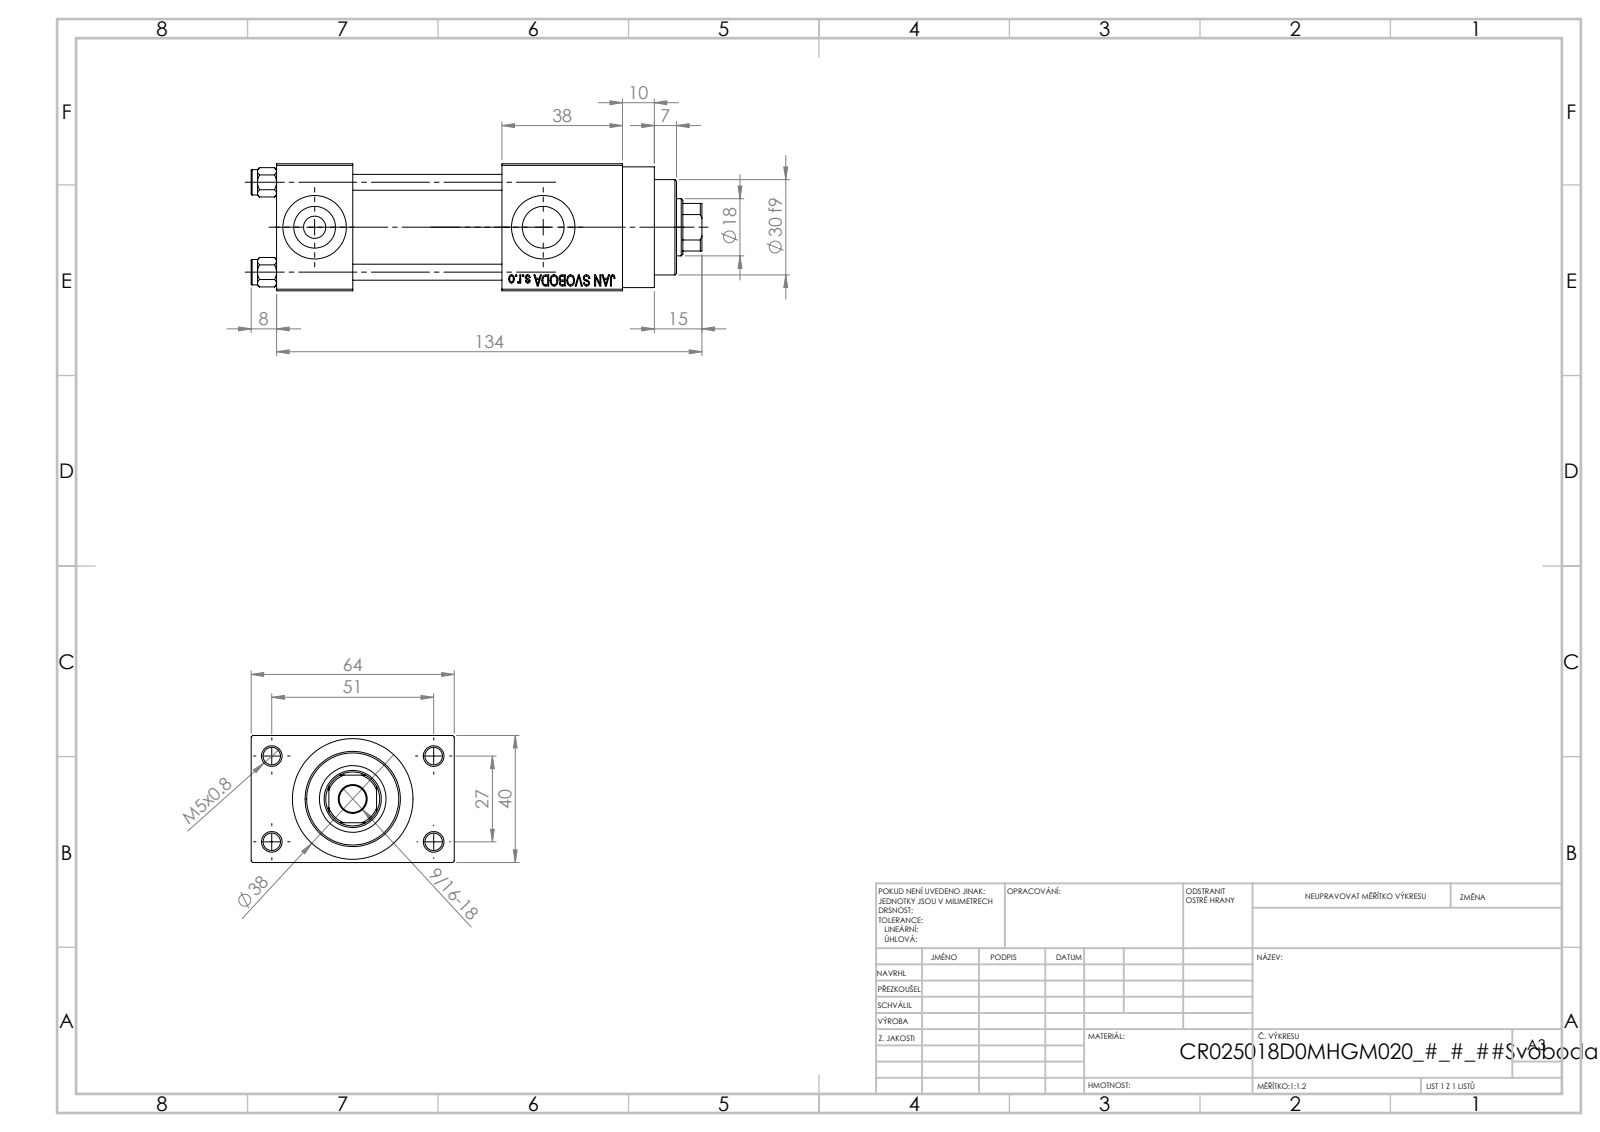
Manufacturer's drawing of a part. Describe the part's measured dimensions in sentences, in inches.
The part is named "V215CR_D_TYCINKA; NUT_M5_D; V215CR_VCP_D; V215_VC_A (+1 more)". Its 3-D file was written by "SolidWorks 2019 (CONFIG_CONTROL_DESIGN)". It is 11 solids with 1099 faces: 495 planar, 86 cylindrical and 518 other. Overall it measures 5.591 by 2.52 by 1.575 inches. Its volume is 10.94 cubic inches and its surface area 100.3 square inches. Round holes: 4 of diameter 0.197, 4 of diameter 0.217, 3 of diameter 0.787, 2 of diameter 0.276, 2 of diameter 0.518, 1 of diameter 0.335, 1 of diameter 0.709, 1 of diameter 0.827, 1 of diameter 0.984, 1 of diameter 1.181. Round bosses or shafts: 4 of diameter 0.315, 1 of diameter 1.496, 1 of diameter 1.22. Partial cylindrical surfaces (rounded edges, fillets, slot ends): 1 of radius 0.335. The main face-to-face distances are 1.575, 0.472, 1.85, 0.945, 2.795, 2.047, 1.496, 4.291, 3.346, 2.52. The hole center spacings are 0.448, 0.788, 1.114, 1.136, 1.177, 1.561, 1.903, 1.063.
